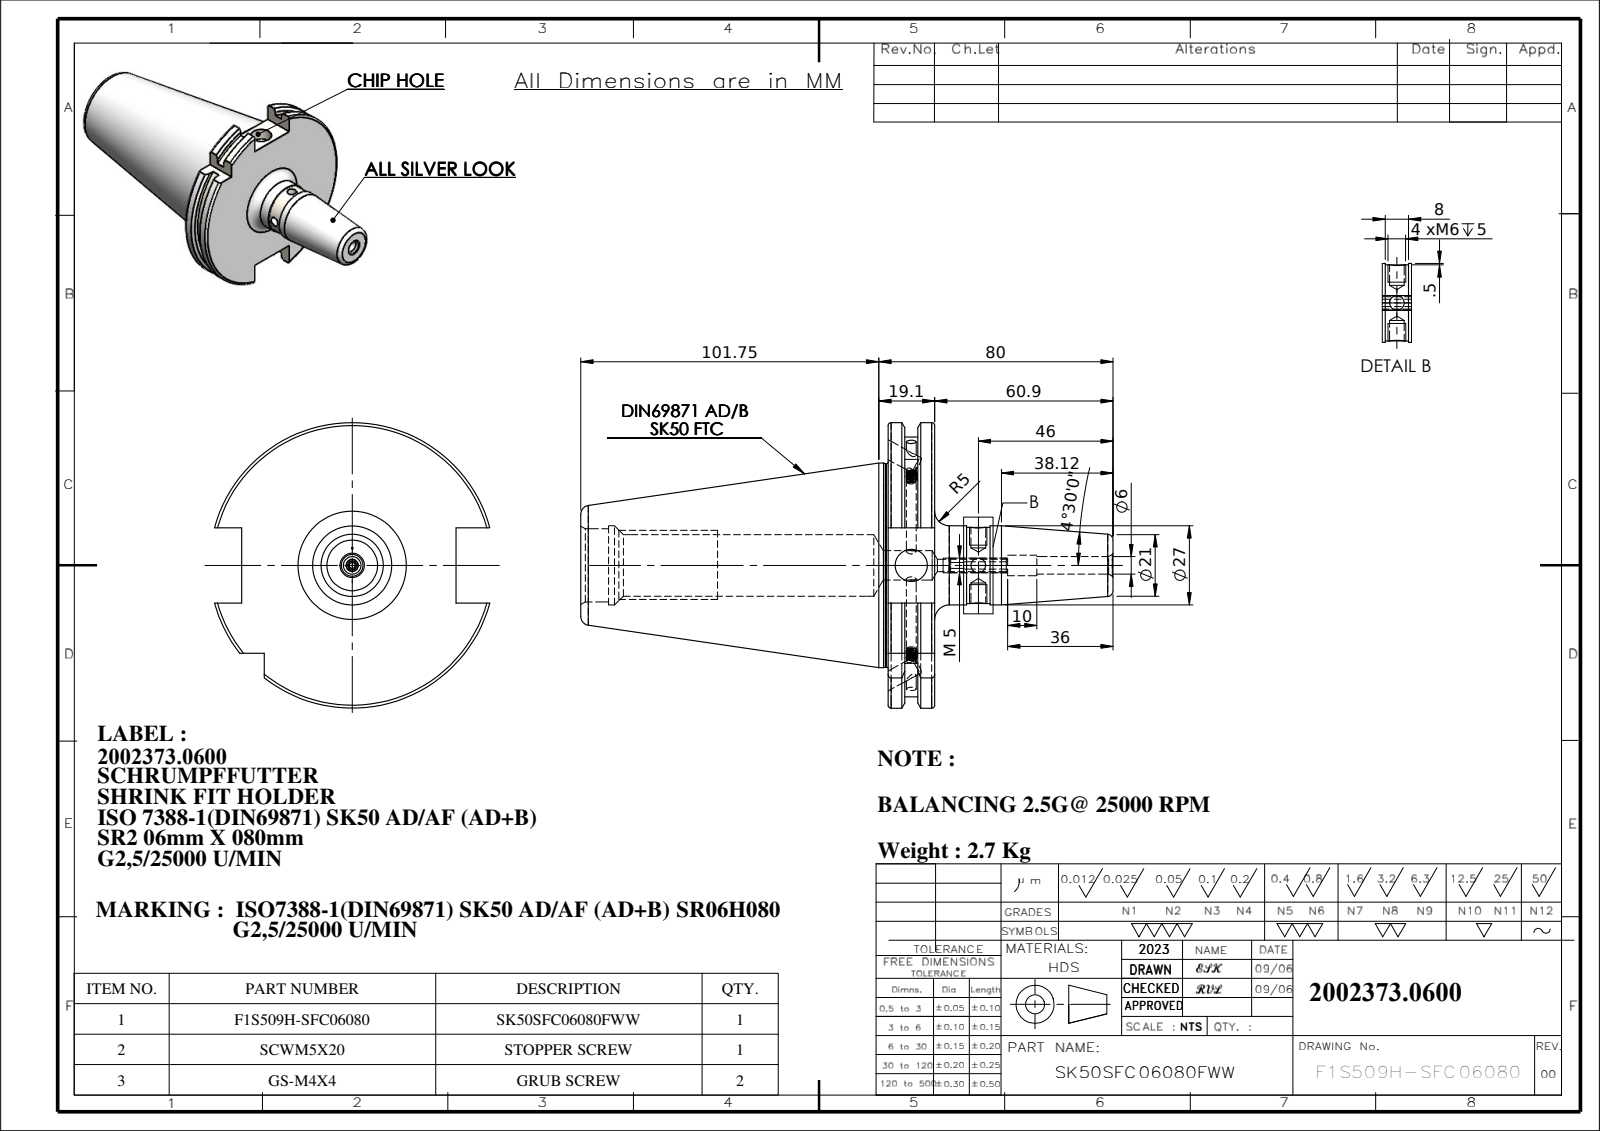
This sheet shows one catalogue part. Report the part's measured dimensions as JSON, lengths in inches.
{"part_name": "SCWM5X20; SK50SFC06080FWW; GS-M4X4_DIN 913 - M4 x 4-N; 91506-SR206080", "step_written_by": "SolidWorks 2018 (CONFIG_CONTROL_DESIGN)", "units": "inches", "bodies": {"solids": 4, "faces": 257, "planar": 60, "cylindrical": 83, "other": 114}, "overall_size": [7.156, 3.839, 3.703], "volume_in3": 21.45, "surface_area_in2": 79.74, "round_holes": [[0.197, 2], [0.236, 2], [0.079, 1], [0.13, 1], [0.165, 1], [0.236, 1], [0.275, 1], [0.394, 1], [0.433, 1], [0.827, 1], [0.984, 1]], "round_bosses_or_shafts": [[0.157, 2], [2.75, 1], [2.734, 1], [1.063, 1], [1.024, 1], [0.197, 1]], "partial_cylinders_radius": [[1.768, 1], [1.919, 1]], "face_to_face_distances": [0.626, 0.223, 0.403, 0.399, 0.176, 0.227, 4.132, 4.355, 4.531, 4.758], "hole_center_spacings": [0.902]}
